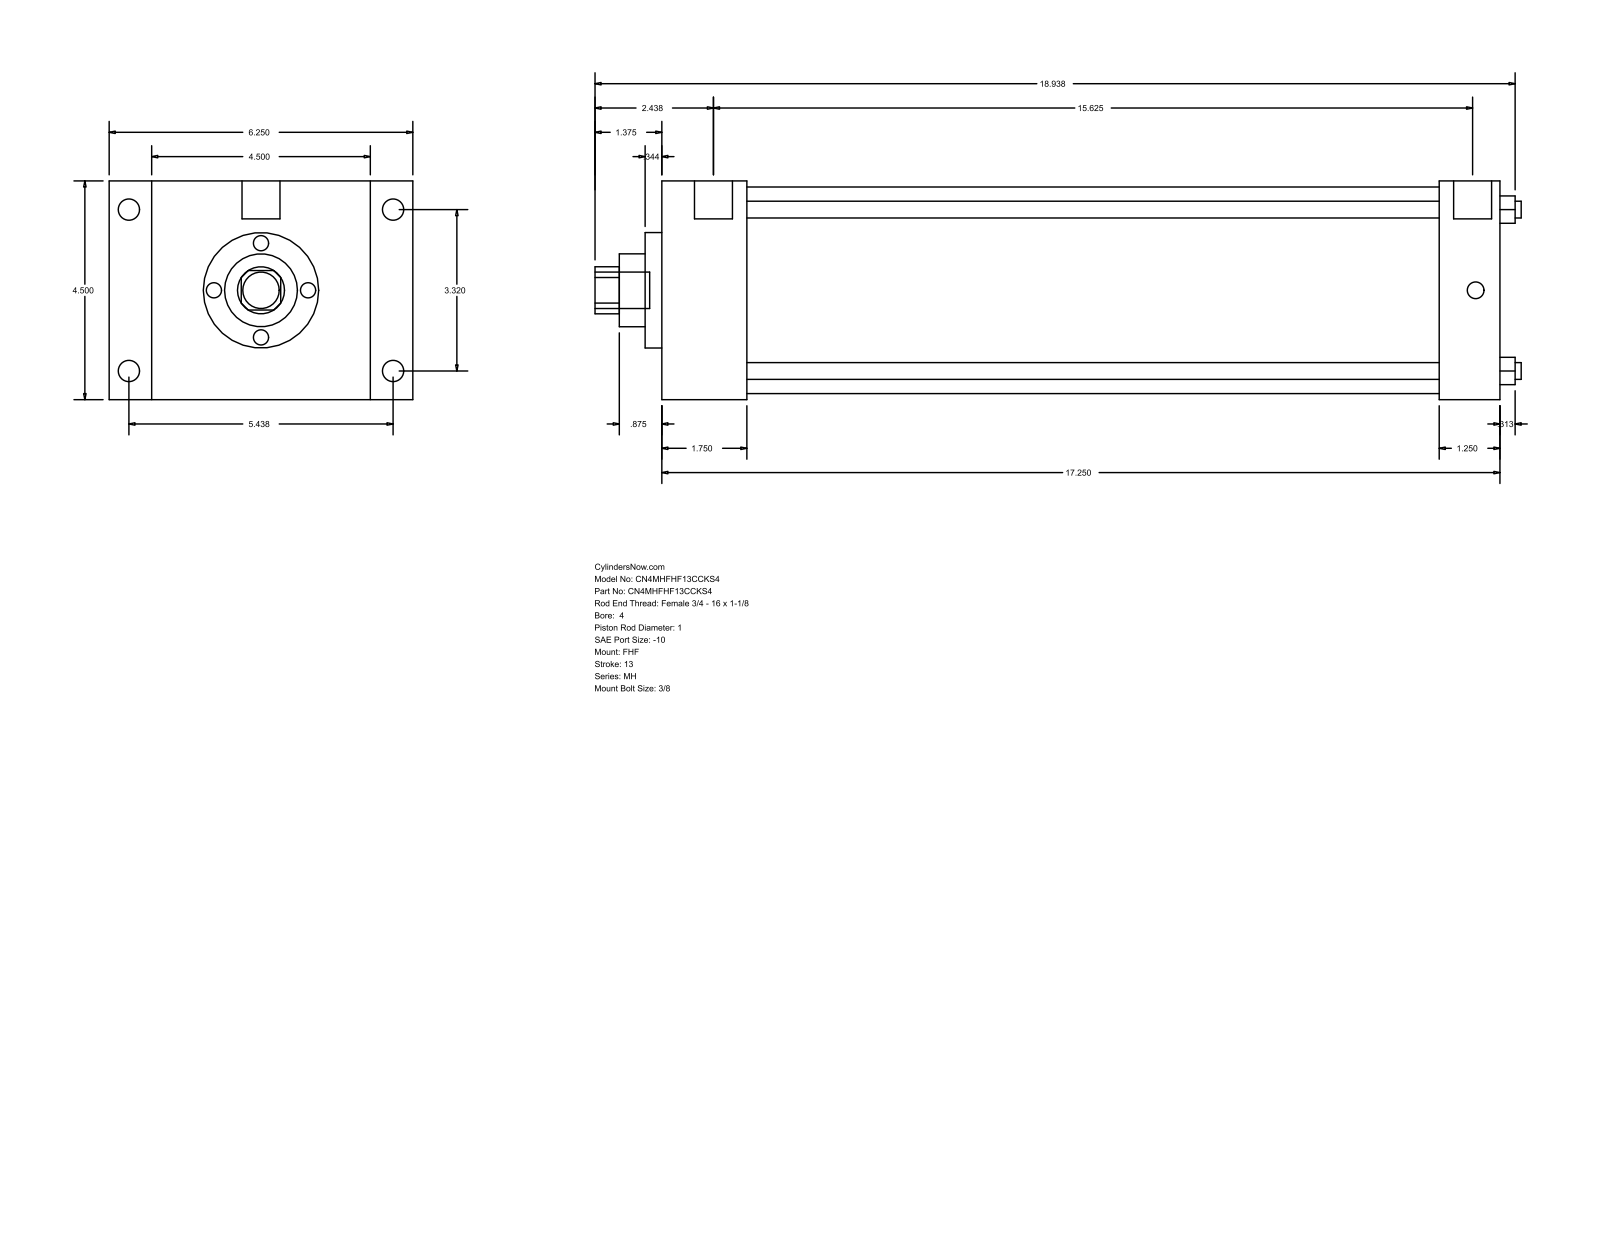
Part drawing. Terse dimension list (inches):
name: MH_FHF__0400_1
written by: GSSL Pune (CONFIG_CONTROL_DESIGN)
unit: in
bodies: 0 solids, 90 faces (61 planar, 29 cylindrical, 0 other)
size: 19.063 × 6.25 × 4.5
holes: 4× ⌀0.345, 1× ⌀1, 1× ⌀1.5, 1× ⌀2.375, 1× ⌀4.25
bosses: 4× ⌀0.438, 4× ⌀0.344, 2× ⌀0.781, 1× ⌀0.75
rounds: 1× R0.484
face distances: 4.5, 17.25, 1.75, 15.5, 0.875, 5.375, 6.25, 16, 14.25, 1.25
hole spacings: 2.347, 3.32, 4.695
